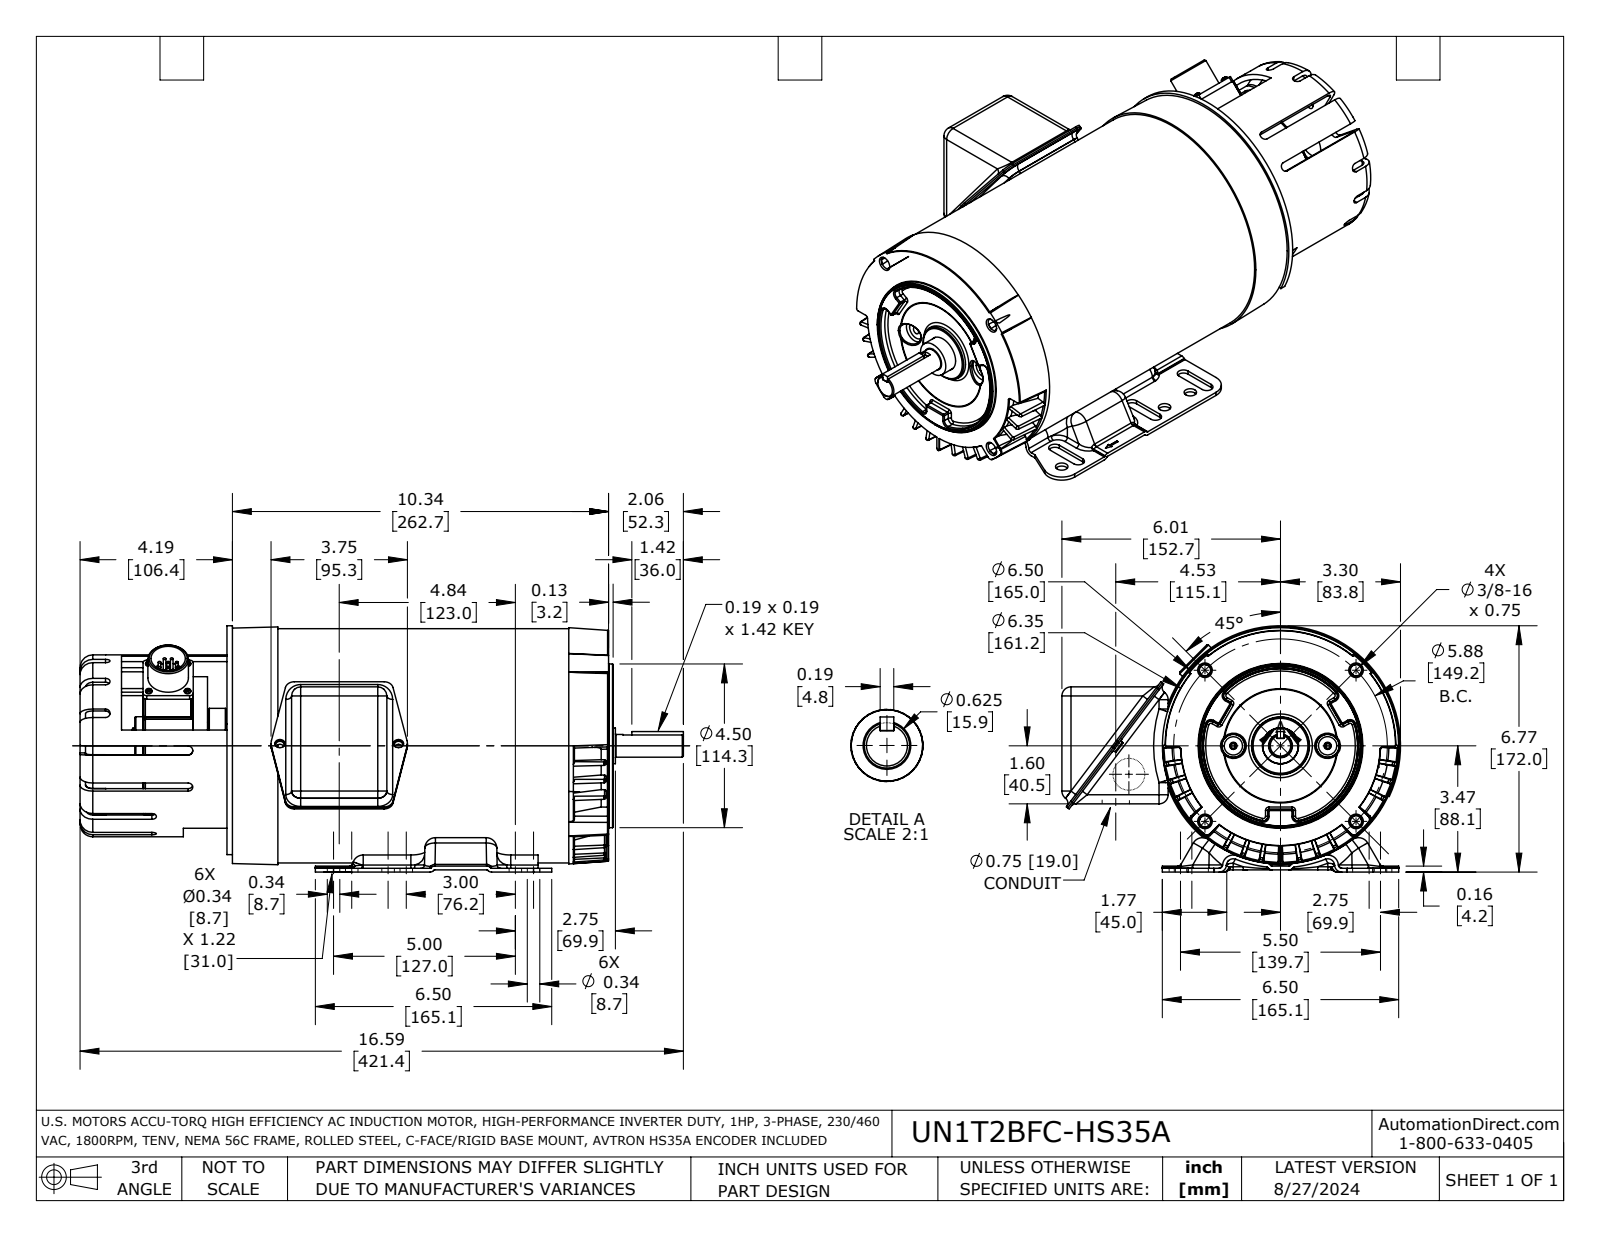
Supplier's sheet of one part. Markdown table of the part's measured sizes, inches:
| quantity | value |
| --- | --- |
| part name | UN1T2BFC-HS35A |
| STEP written by | SolidWorks 2021 (AUTOMOTIVE_DESIGN) |
| units | inches |
| bodies | 26 solids, 3051 faces (756 planar, 717 cylindrical, 1578 other) |
| overall size | 16.591 × 9.311 × 6.77 |
| volume | 102.5 in³ |
| surface area | 1 166 in² |
| round holes (diameter × count) | 0.25 × 8, 0.344 × 6, 0.4 × 6, 0.12 × 4, 0.2 × 4, 0.302 × 4, 0.421 × 4, 0.55 × 4, 0.136 × 3, 0.098 × 2, 0.173 × 2, 0.229 × 2 |
| round bosses / shafts (diameter × count) | 0.072 × 8, 0.175 × 4, 0.12 × 4, 0.15 × 3, 0.325 × 2, 0.072 × 2, 6.44 × 1, 6.315 × 1 |
| partial cylindrical surfaces (radius × count) | 0.062 × 91, 0.031 × 71, 0.125 × 42, 0.25 × 26, 0.202 × 18, 0.094 × 13, 0.048 × 12, 0.172 × 12 |
| main face-to-face distances | 0.048, 1.08, 1.375, 2.455, 0.15, 4.04, 0.104, 0.12, 0.53, 0.06 |
| hole center spacings | 2.098, 2.246, 3.419, 4.349, 5.422, 2.073, 2.232, 2.234 |
